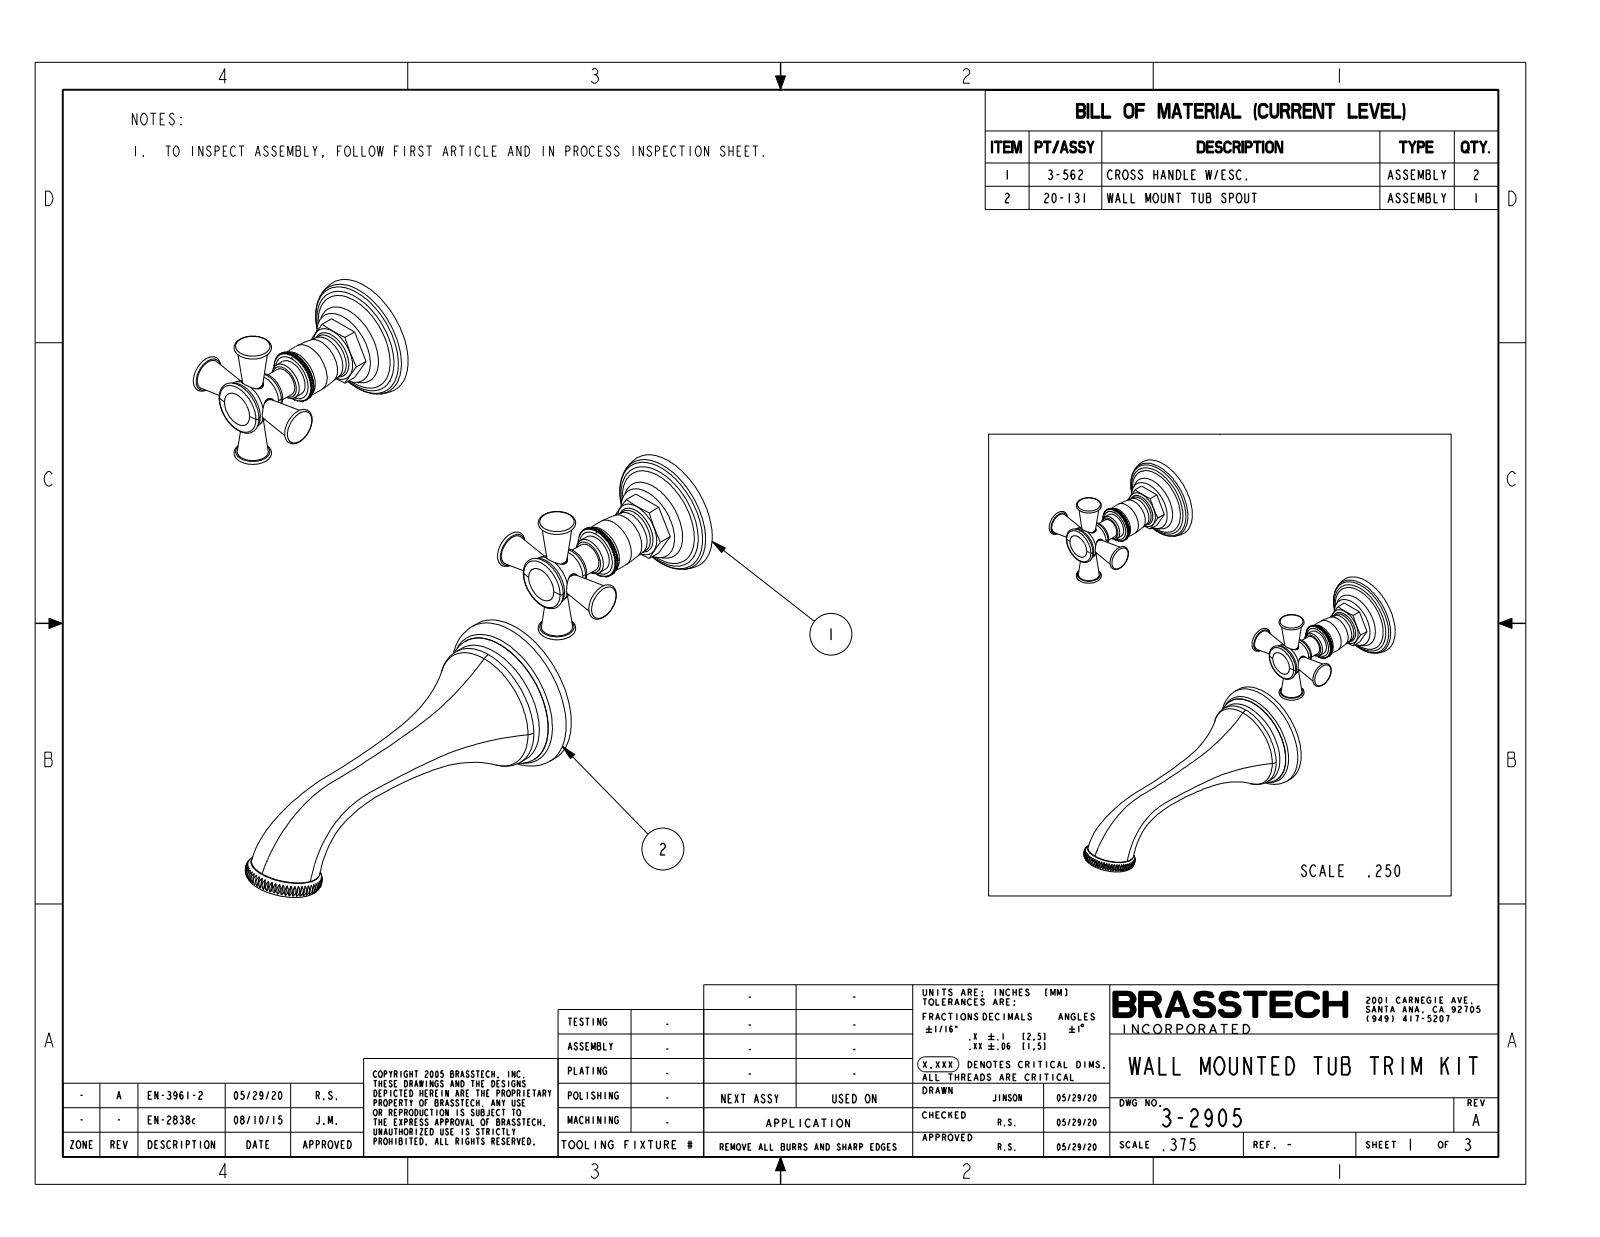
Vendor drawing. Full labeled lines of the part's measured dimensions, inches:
Part name (STEP PRODUCT): 3-2905_SW0003
STEP written by: CREO PARAMETRIC BY PTC INC, 2018400 (AUTOMOTIVE_DESIGN)
Units: inches
Bodies: 3 solids, 932 faces (534 planar, 22 cylindrical, 376 other)
Overall size (bounding box): 10.325 × 8.853 × 6.711
Volume: 18.07 in³ · Surface area: 89.87 in²
Round bosses / shafts (diameter × count): ⌀0.82 ×2, ⌀0.686 ×2, ⌀0.53 ×2, ⌀2.85 ×1, ⌀2.506 ×1, ⌀2.345 ×1, ⌀1.198 ×1, ⌀1.102 ×1
Main face-to-face distances: 0.534, 0.544, 1.025, 6.82, 0.575, 0.041, 0.031, 1.874, 1.34, 1.33
